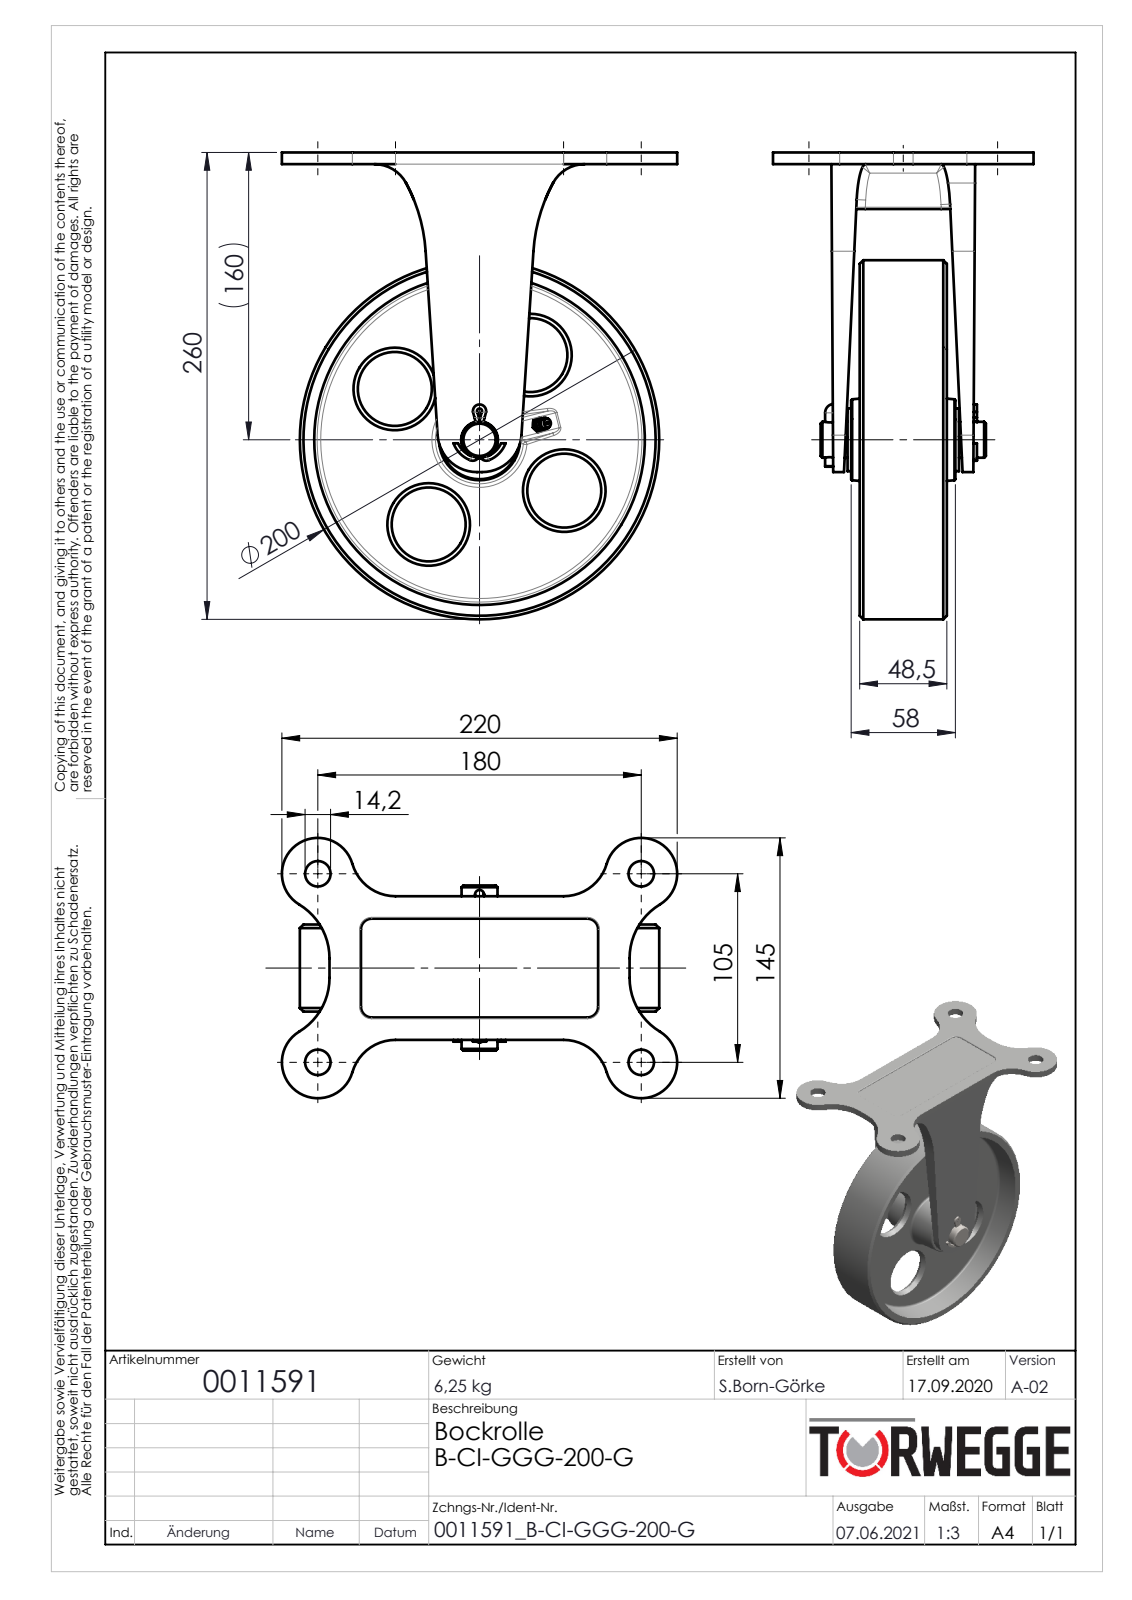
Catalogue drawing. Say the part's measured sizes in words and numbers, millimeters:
The part is named "0011591". Its 3-D file was written by "SolidWorks 2020 (AUTOMOTIVE_DESIGN)". It is 8 solids with 285 faces: 84 planar, 105 cylindrical and 96 other. Overall it measures 260 by 220 by 145 millimeters. Its volume is 859 689 cubic millimeters and its surface area 213 673 square millimeters. Round holes: 4 of diameter 14.2, 2 of diameter 5, 1 of diameter 6, 1 of diameter 20, 1 of diameter 20.5, 1 of diameter 25. Round bosses or shafts: 1 of diameter 200, 1 of diameter 35, 1 of diameter 5. Partial cylindrical surfaces (rounded edges, fillets, slot ends): 6 of radius 5, 6 of radius 20, 4 of radius 0.75, 4 of radius 6, 4 of radius 25, 4 of radius 35, 3 of radius 1.42, 3 of radius 1.5. The main face-to-face distances are 8, 6.5, 1, 5.5, 20.25, 28.25, 48.5, 25, 33, 4.75. The hole center spacings are 90.73, 91.01, 105, 128.34, 129.78, 180, 208.39, 80.
